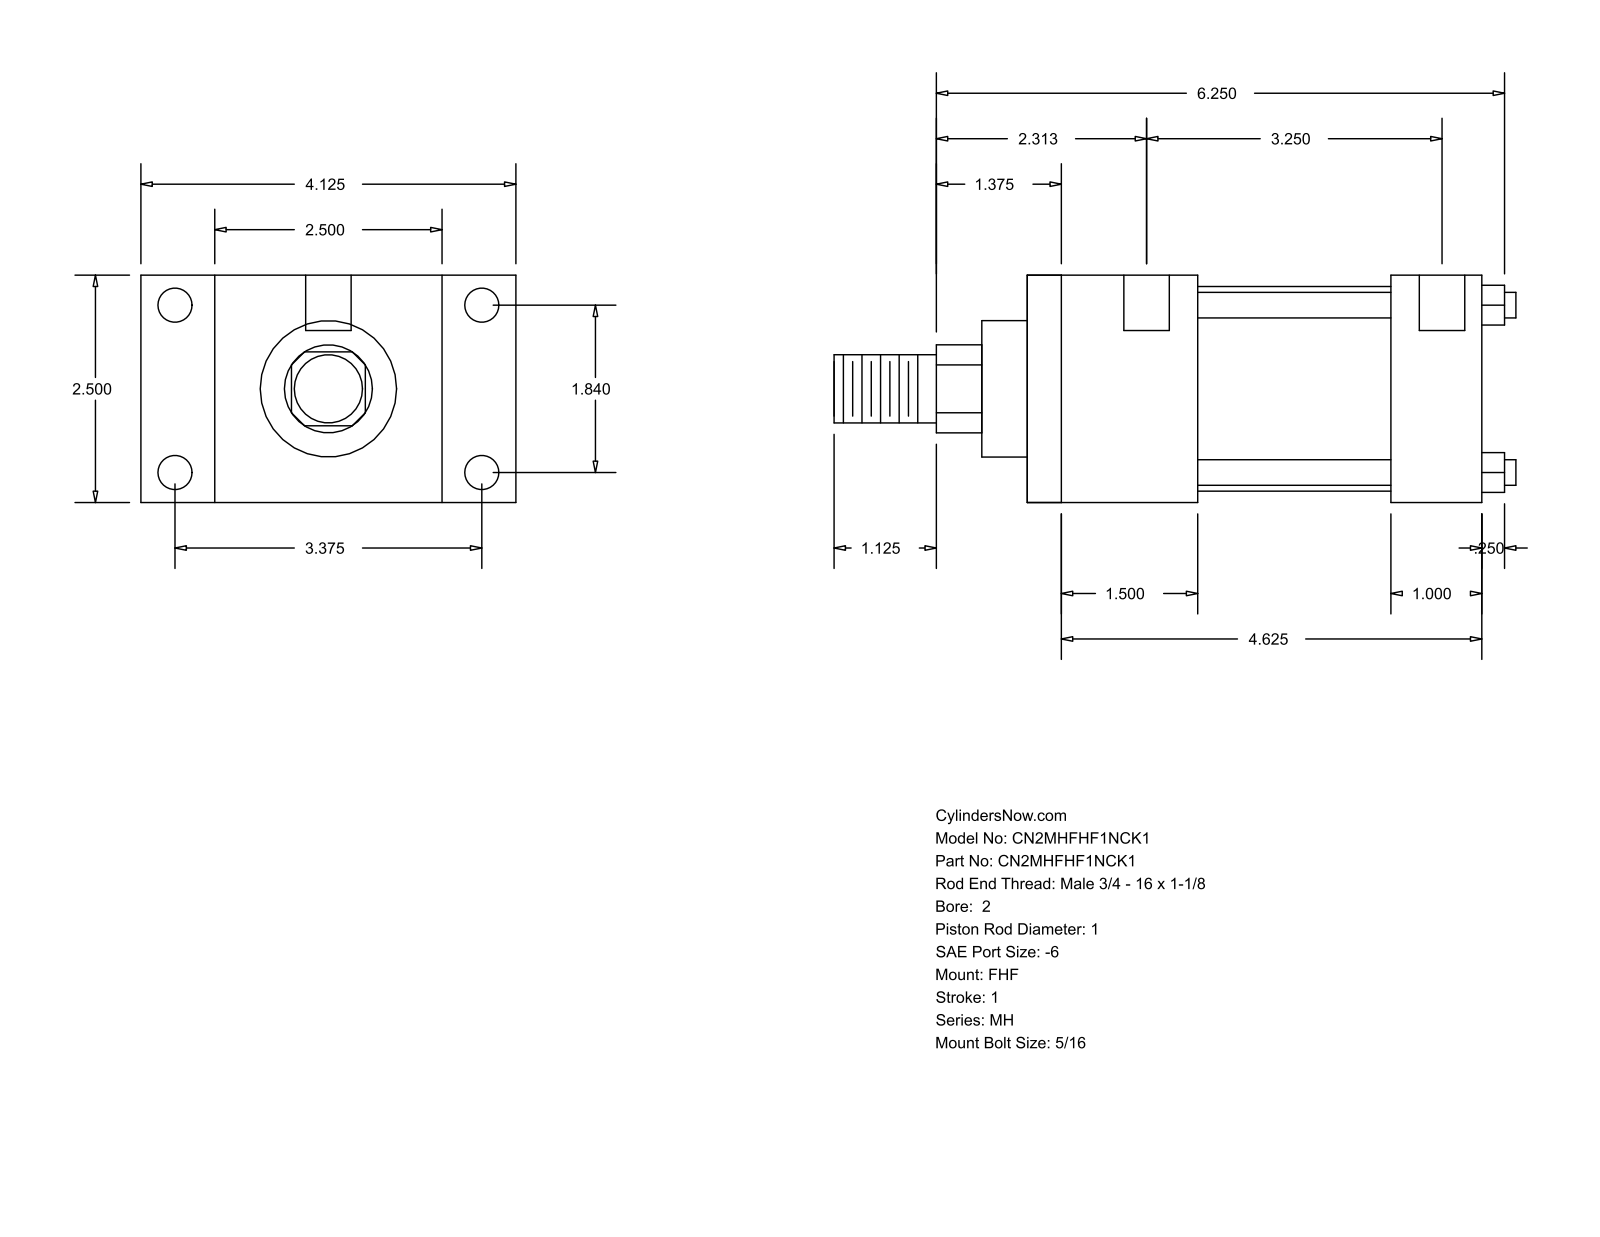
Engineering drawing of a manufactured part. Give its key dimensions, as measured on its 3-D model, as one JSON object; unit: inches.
{"part_name": "MH_FHF__0200_1", "step_written_by": "GSSL Pune (CONFIG_CONTROL_DESIGN)", "units": "inches", "bodies": {"solids": 0, "faces": 88, "planar": 60, "cylindrical": 28, "other": 0}, "overall_size": [7.5, 4.125, 2.5], "round_holes": [[0.219, 4], [0.375, 4], [0.5, 2]], "round_bosses_or_shafts": [[0.281, 4], [2.25, 1], [1.5, 1], [1, 1], [0.75, 1]], "partial_cylinders_radius": [[0.484, 1]], "face_to_face_distances": [2.5, 5, 1.875, 3.125, 0.813, 3.313, 4.125, 2.125, 4, 1], "hole_center_spacings": [3.375, 1.84, 3.562, 3.844, 0.125, 0.187, 3.25, 3.437]}
